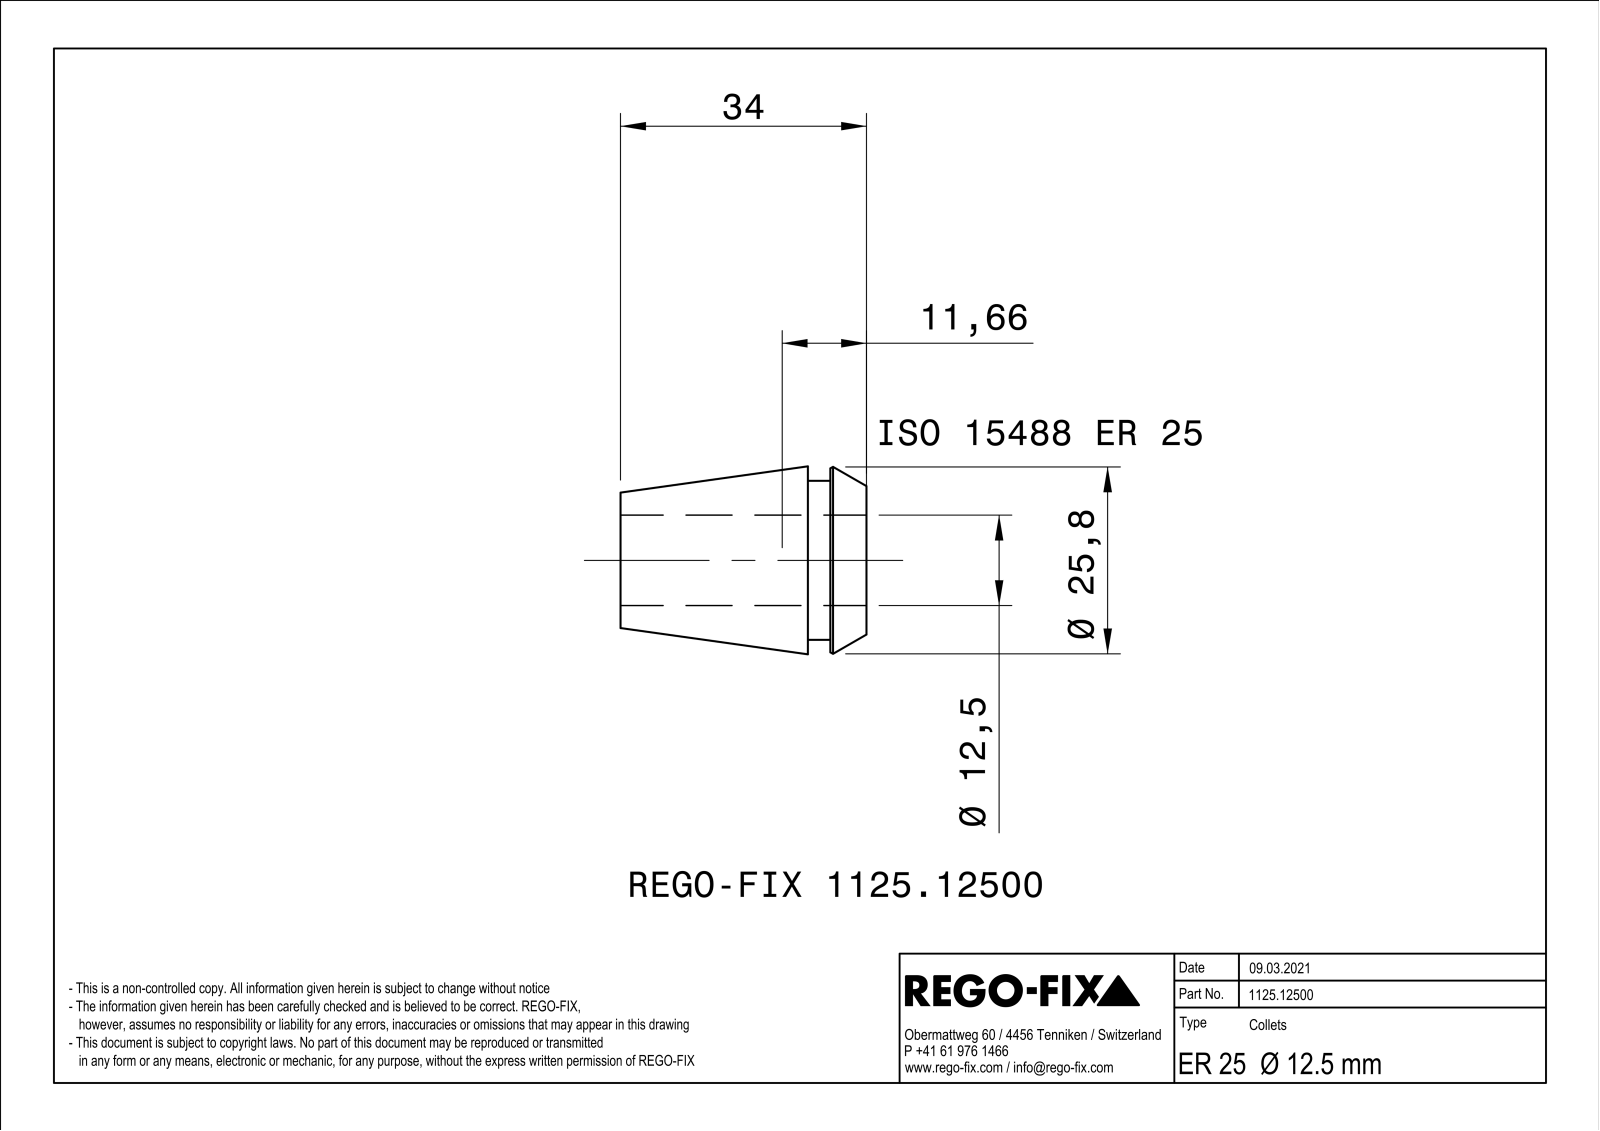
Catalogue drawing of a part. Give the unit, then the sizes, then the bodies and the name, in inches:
Units: inches
Overall size (bounding box): 1.339 × 1.023 × 1.023
Round holes (diameter × count): ⌀0.492 ×1
Round bosses / shafts (diameter × count): ⌀0.866 ×1
Partial cylindrical surfaces — rounded edges, fillets, slot ends (radius × count): R0.016 ×8
Main face-to-face distances: 0.031, 0.319, 1.339, 1.02, 0.197, 0.122, 1.142
Volume: 0.458 in³ · Surface area: 13.03 in²
Bodies: 1 solid, 177 faces (72 planar, 25 cylindrical, 80 other)
Part name (STEP PRODUCT): NOCUT
STEP written by: SIEMENS PLM Software Solid Edge ST10 (AUTOMOTIVE_DESIGN)
